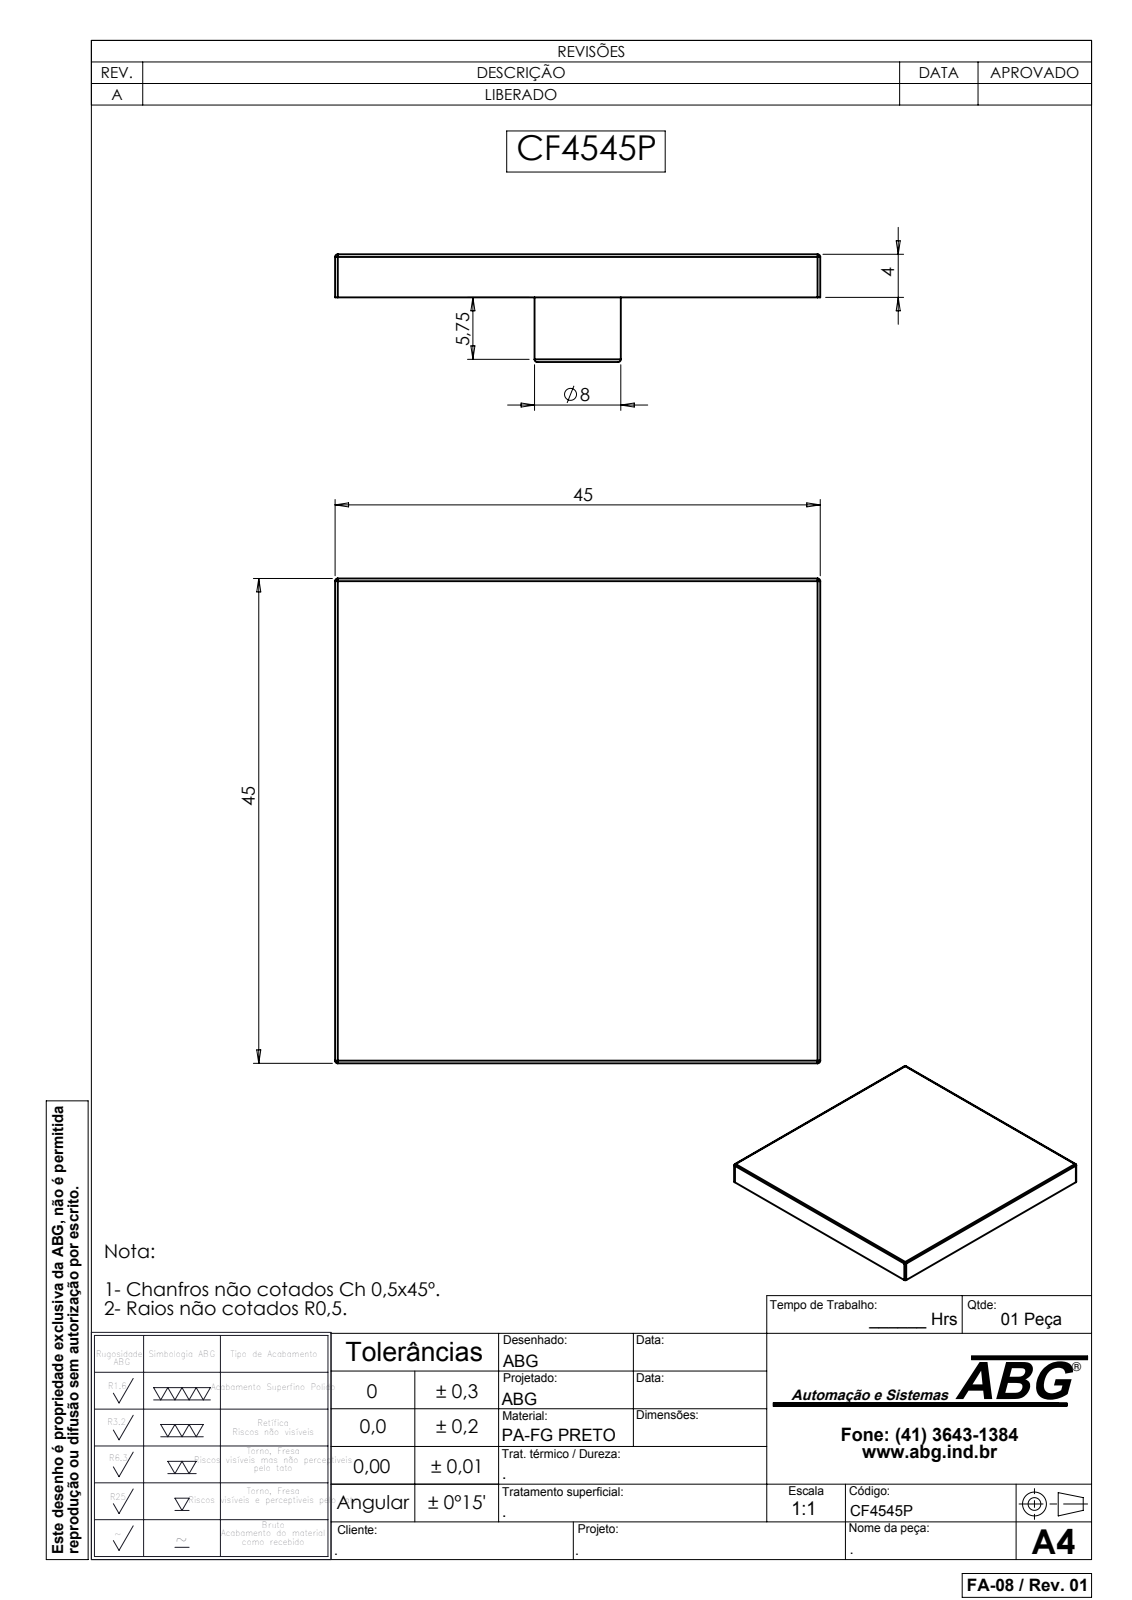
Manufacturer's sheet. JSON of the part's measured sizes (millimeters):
{"part_name": "CF4545P", "step_written_by": "SolidWorks 2007 (CONFIG_CONTROL_DESIGN)", "units": "millimeters", "bodies": {"solids": 1, "faces": 28, "planar": 8, "cylindrical": 12, "other": 8}, "overall_size": [45, 45, 10], "volume_mm3": 8229, "surface_area_mm2": 5008, "round_holes": [[6, 1]], "round_bosses_or_shafts": [[8, 1]], "partial_cylinders_radius": [[0.25, 8]], "face_to_face_distances": [4, 45, 10, 6]}
